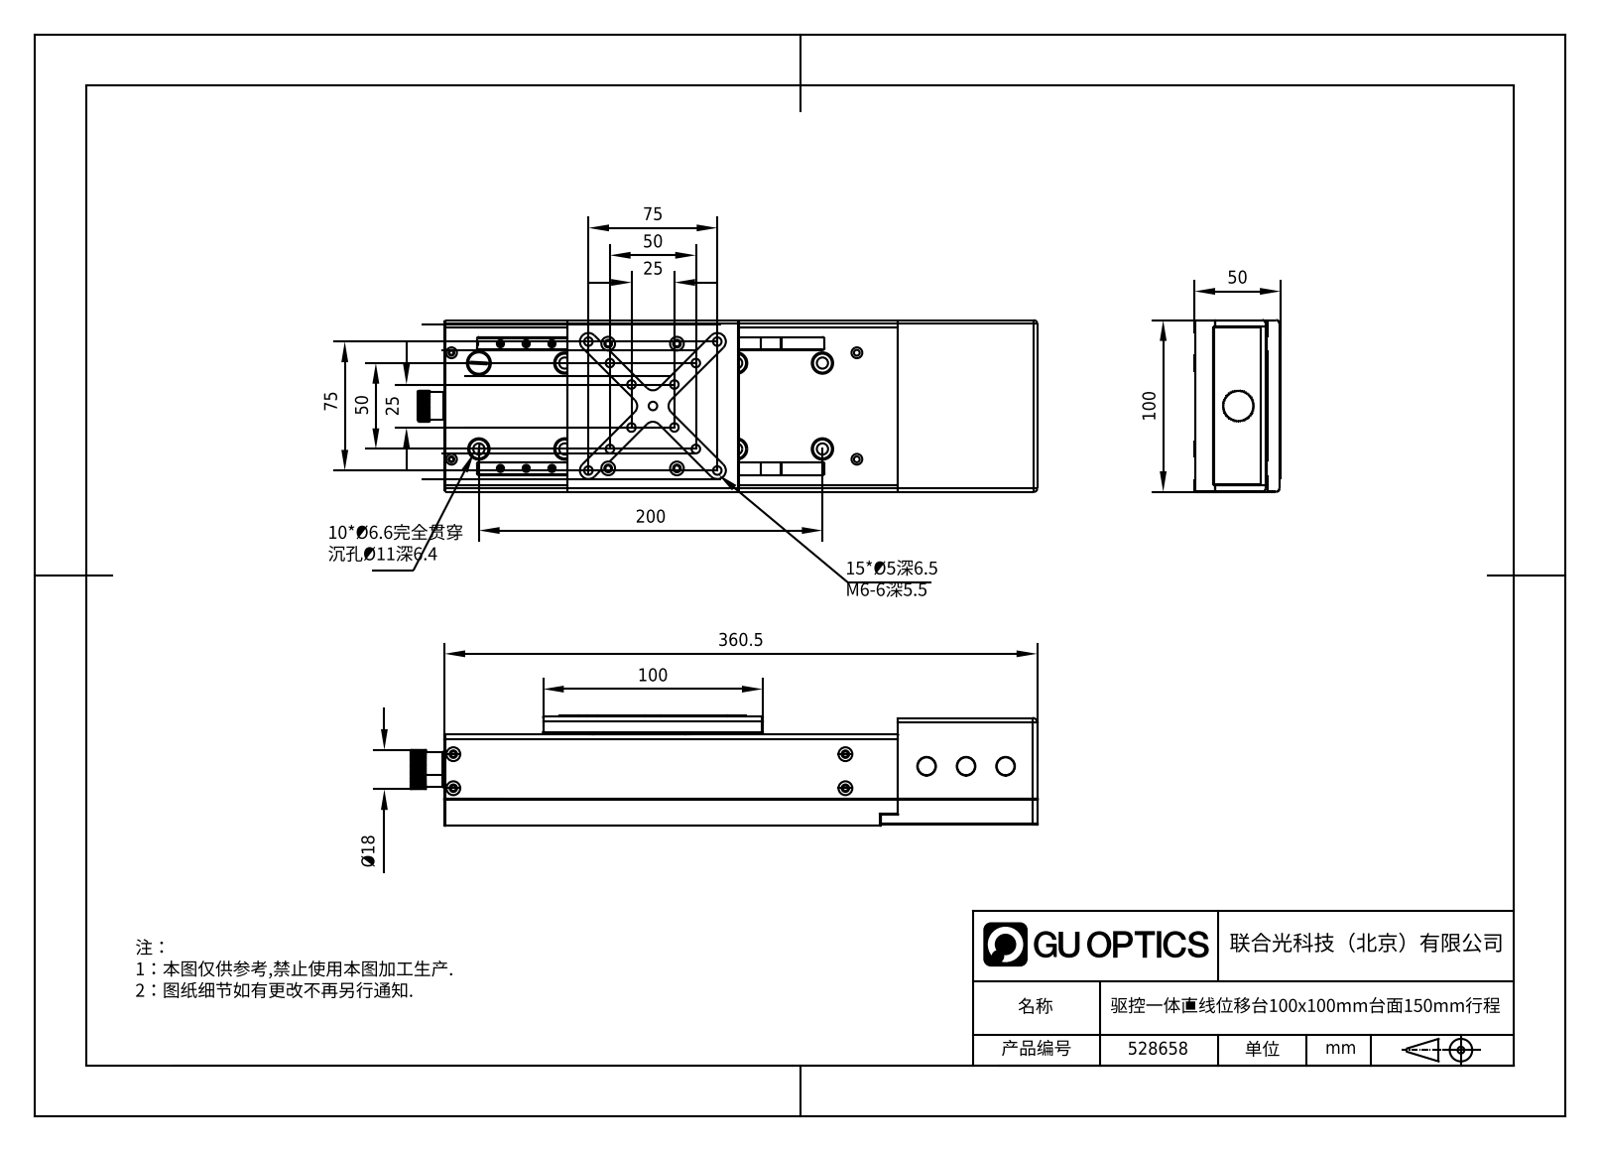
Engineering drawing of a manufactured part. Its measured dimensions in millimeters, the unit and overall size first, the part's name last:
Units: millimetres
Overall size (bounding box): 360.5 × 100 × 50
Round holes (diameter × count): ⌀2.4 ×32, ⌀2.5 ×21, ⌀3.4 ×21, ⌀4.2 ×18, ⌀1.57 ×17, ⌀1.6 ×16, ⌀4.4 ×16, ⌀5 ×14, ⌀6.6 ×10, ⌀11 ×10, ⌀12.5 ×10, ⌀6.5 ×9
Round bosses / shafts (diameter × count): ⌀2.2 ×4, ⌀14 ×2, ⌀3.8 ×2, ⌀2 ×2, ⌀22 ×1, ⌀16 ×1, ⌀13 ×1, ⌀3 ×1
Partial cylindrical surfaces — rounded edges, fillets, slot ends (radius × count): R2 ×29, R1 ×20, R5 ×12, R0.7 ×4, R1.35 ×4, R0.3 ×2, R0.4 ×2, R0.5 ×2
Main face-to-face distances: 4, 38, 26.5, 11.5, 1, 3, 0.5, 30.5, 7, 8
Hole centre spacings: 17.68, 35.36, 10.5, 55.9, 39.53, 53.03, 63.74, 15
Volume: 945 927 mm³ · Surface area: 325 787 mm²
Bodies: 47 solids, 2408 faces (1230 planar, 816 cylindrical, 362 other)
Part name (STEP PRODUCT): 528658
STEP written by: SolidWorks 2020 (CONFIG_CONTROL_DESIGN)
